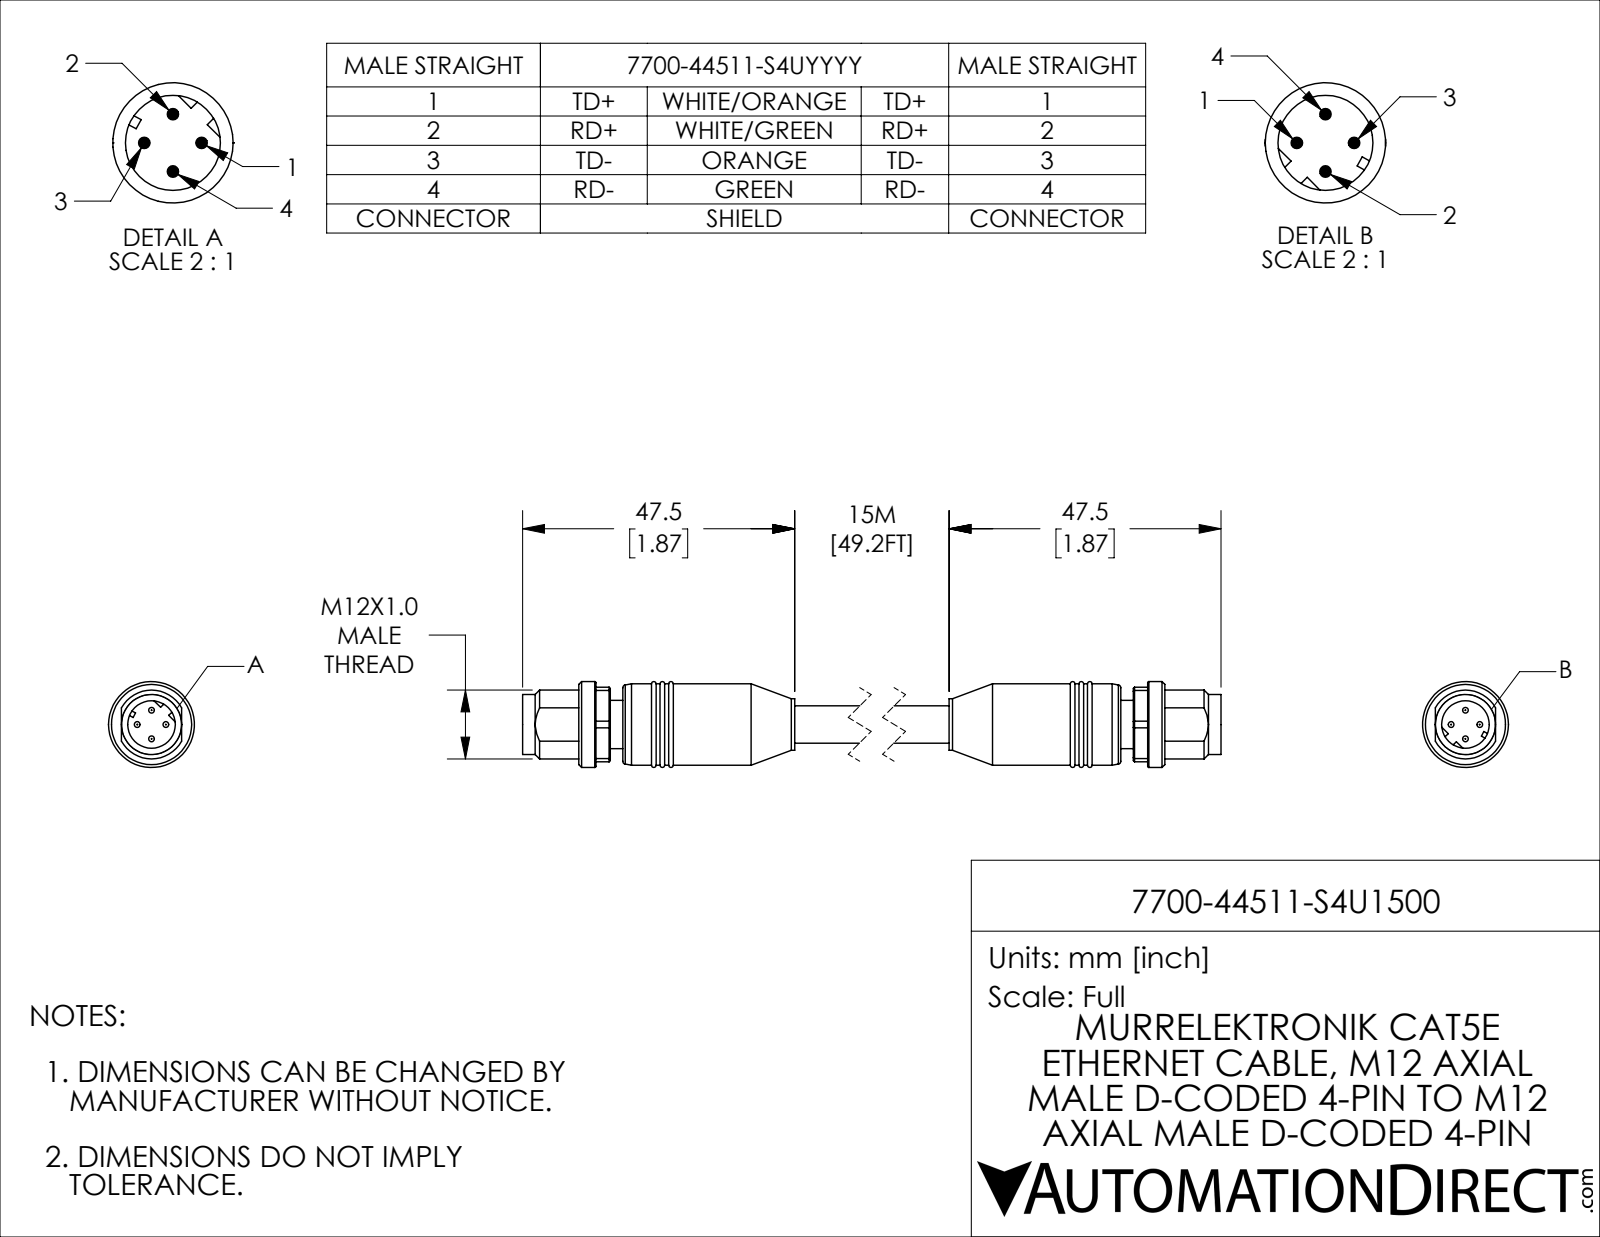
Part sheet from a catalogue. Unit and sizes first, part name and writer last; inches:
Units: inches
Overall size (bounding box): 5.815 × 0.591 × 0.591
Round holes (diameter × count): ⌀0.327 ×1
Round bosses / shafts (diameter × count): ⌀0.039 ×4, ⌀0.591 ×1, ⌀0.559 ×1, ⌀0.413 ×1, ⌀0.354 ×1, ⌀0.331 ×1, ⌀0.256 ×1
Partial cylindrical surfaces — rounded edges, fillets, slot ends (radius × count): R0.236 ×1, R0.283 ×1
Main face-to-face distances: 0.087, 4.524, 0.035, 0.252, 0.339, 4.776, 4.862, 5.079, 0.217, 0.303
Volume: 0.804 in³ · Surface area: 9.846 in²
Bodies: 2 solids, 226 faces (72 planar, 74 cylindrical, 80 other)
Part name (STEP PRODUCT): 7700-44511-S4U1500; 7700-44511-S4U1500_1
STEP written by: SolidWorks 2021 (CONFIG_CONTROL_DESIGN)
